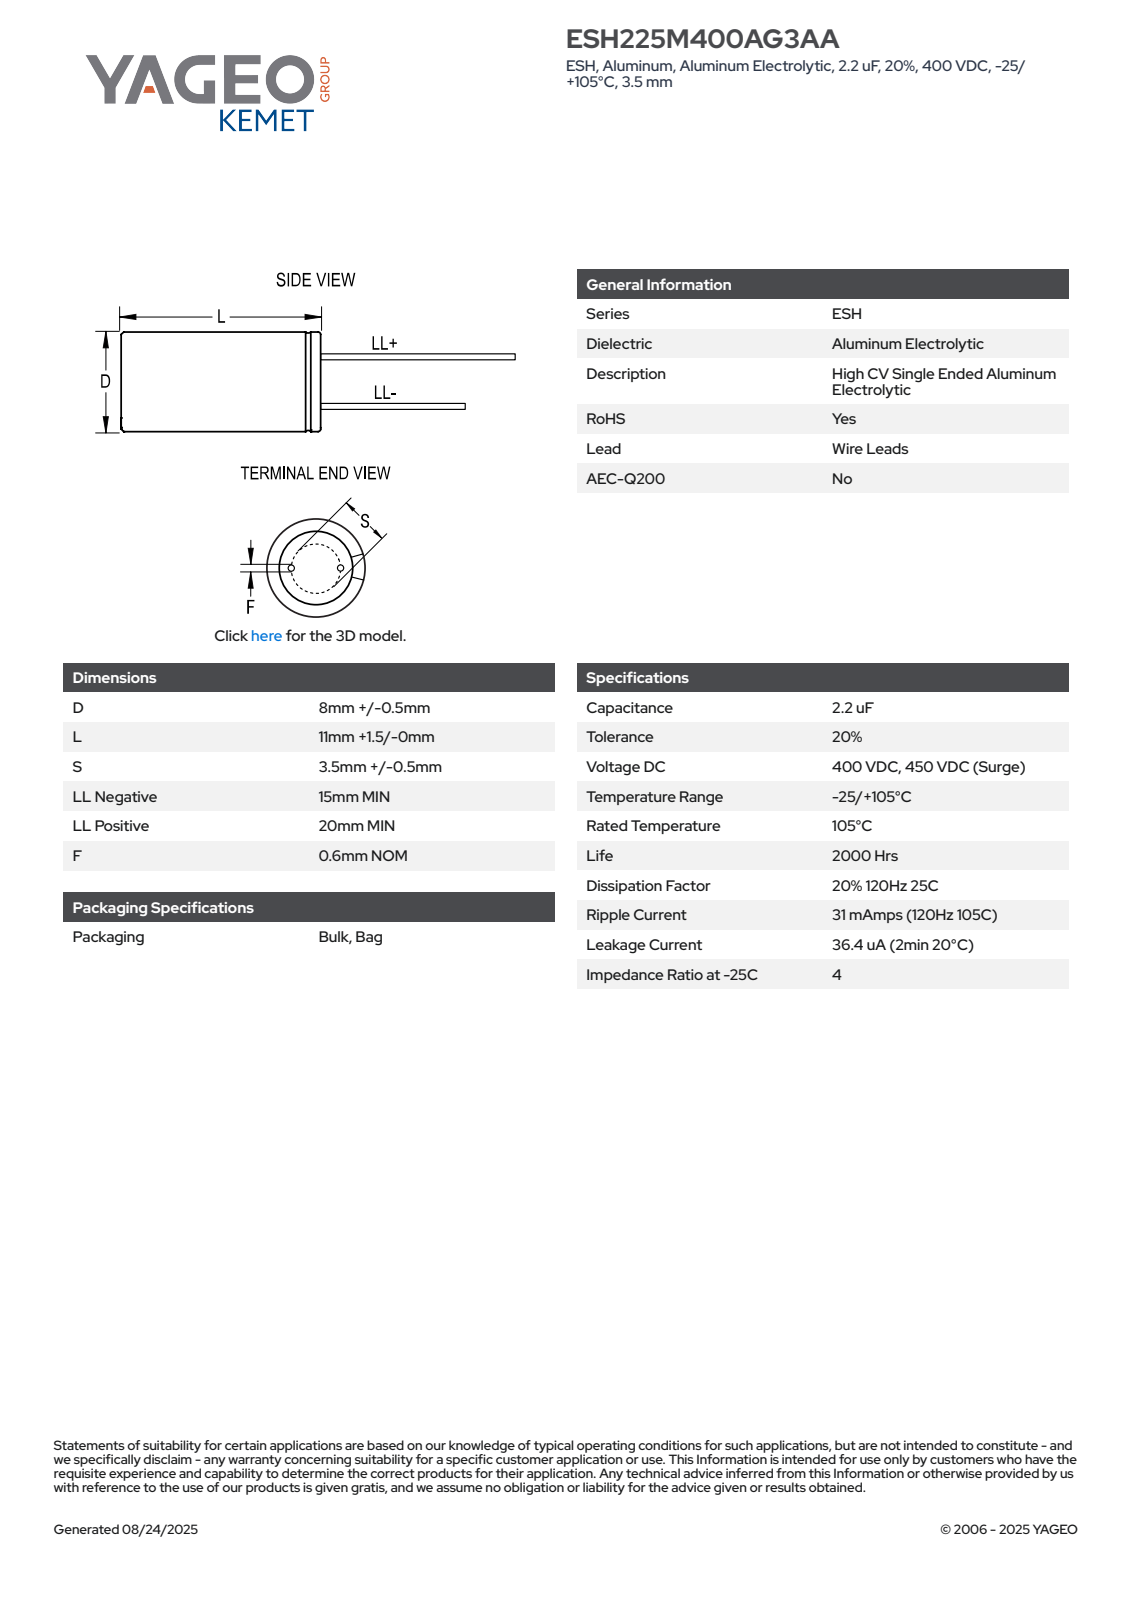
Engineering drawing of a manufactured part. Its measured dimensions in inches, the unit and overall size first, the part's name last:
Units: inches
Overall size (bounding box): 1.28 × 0.335 × 0.335
Round bosses / shafts (diameter × count): ⌀0.024 ×2, ⌀0.335 ×1
Main face-to-face distances: 0.492, 0.493, 1.083, 1.28, 1.083, 1.28, 0.591, 0.787, 0.197, 0.045
Volume: 0.044 in³ · Surface area: 0.82 in²
Bodies: 4 solids, 75 faces (61 planar, 8 cylindrical, 6 other)
Part name (STEP PRODUCT): CAR_KLP_8X11_D8.5L12.5S3.5F0.6
STEP written by: SolidWorks 2014 (AUTOMOTIVE_DESIGN)
